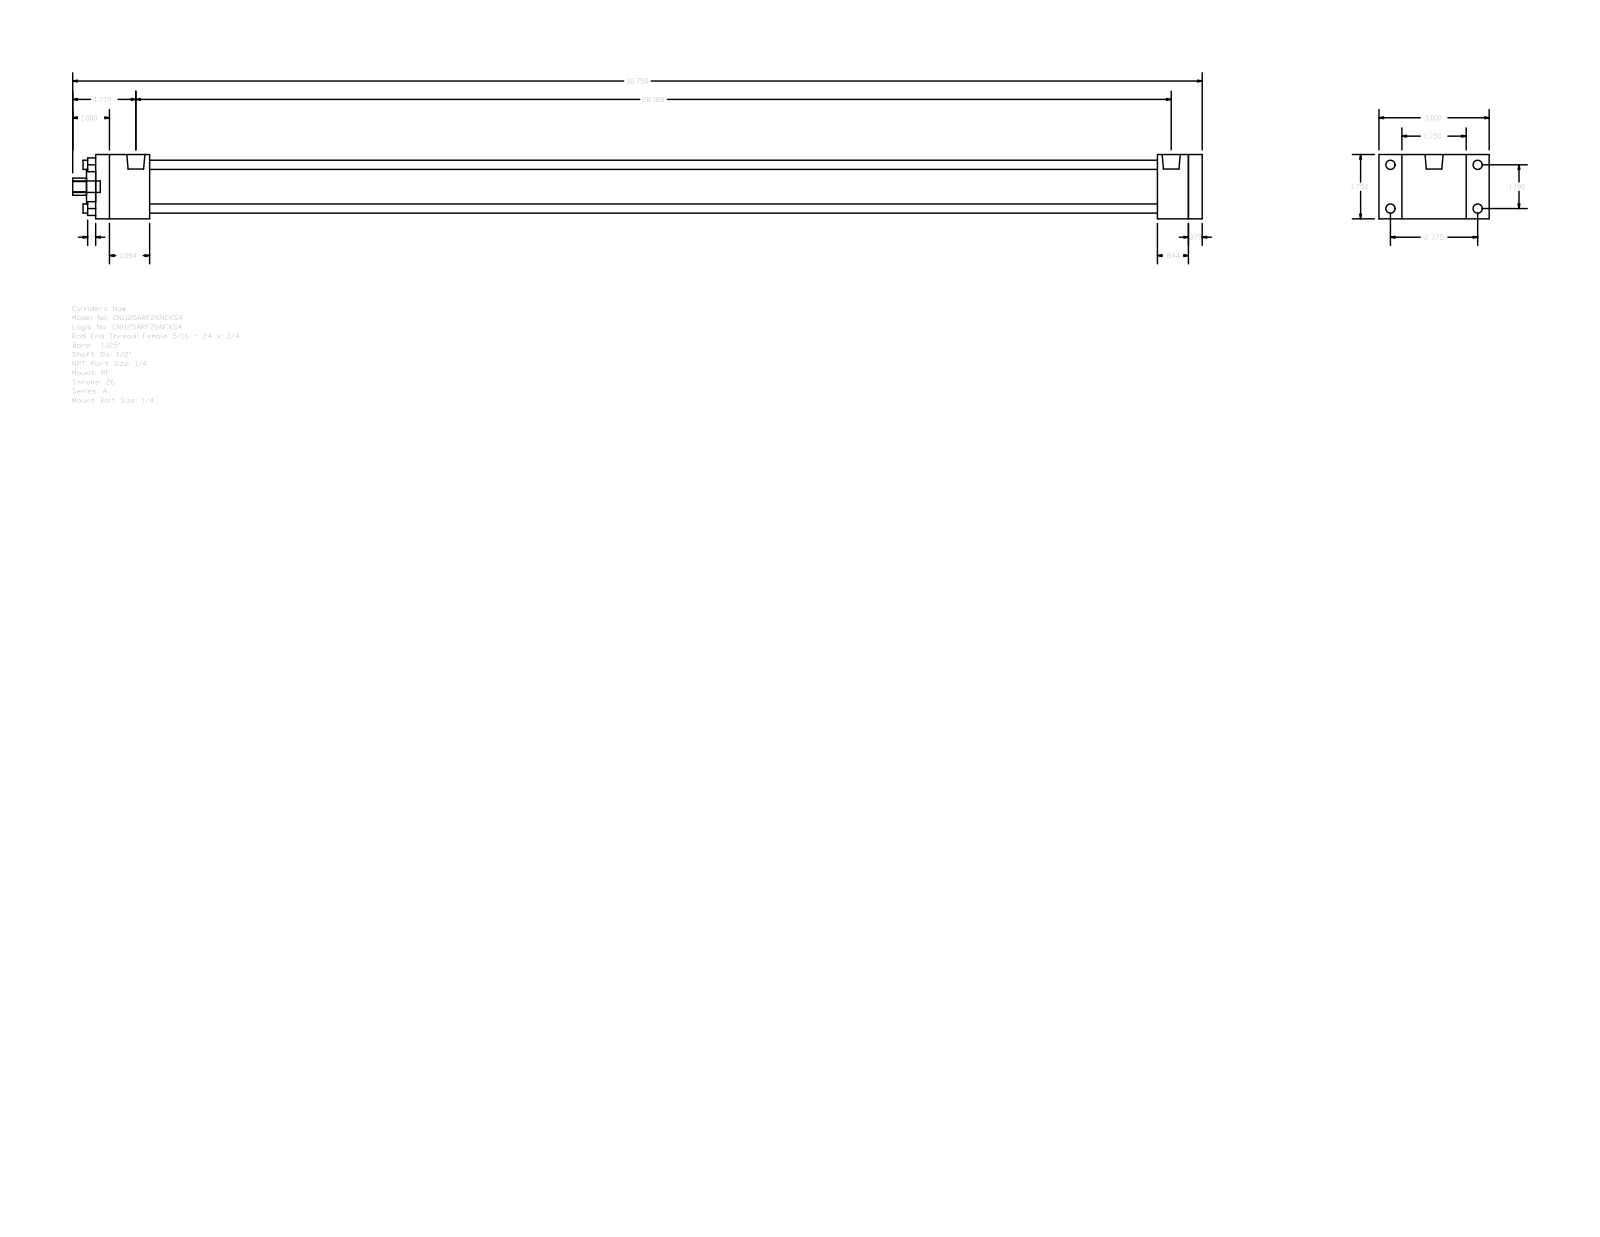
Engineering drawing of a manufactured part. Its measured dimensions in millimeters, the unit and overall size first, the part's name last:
Units: millimetres
Overall size (bounding box): 781.05 × 76.2 × 44.45
Round holes (diameter × count): ⌀6.35 ×4, ⌀12.7 ×1, ⌀23.81 ×1, ⌀31.88 ×1
Round bosses / shafts (diameter × count): ⌀6.35 ×4, ⌀5.56 ×4, ⌀12.49 ×2, ⌀7.94 ×1
Partial cylindrical surfaces — rounded edges, fillets, slot ends (radius × count): R5.94 ×1
Main face-to-face distances: 44.46, 9.53, 765.17, 755.64, 37.3, 734.21, 696.91, 718.34, 727.87, 21.43
Hole centre spacings: 21.37, 30.22, 42.74
Bodies: 0 solids, 92 faces (64 planar, 28 cylindrical, 0 other)
Part name (STEP PRODUCT): A_RF__0112_0.5
STEP written by: GSSL Pune (CONFIG_CONTROL_DESIGN)
